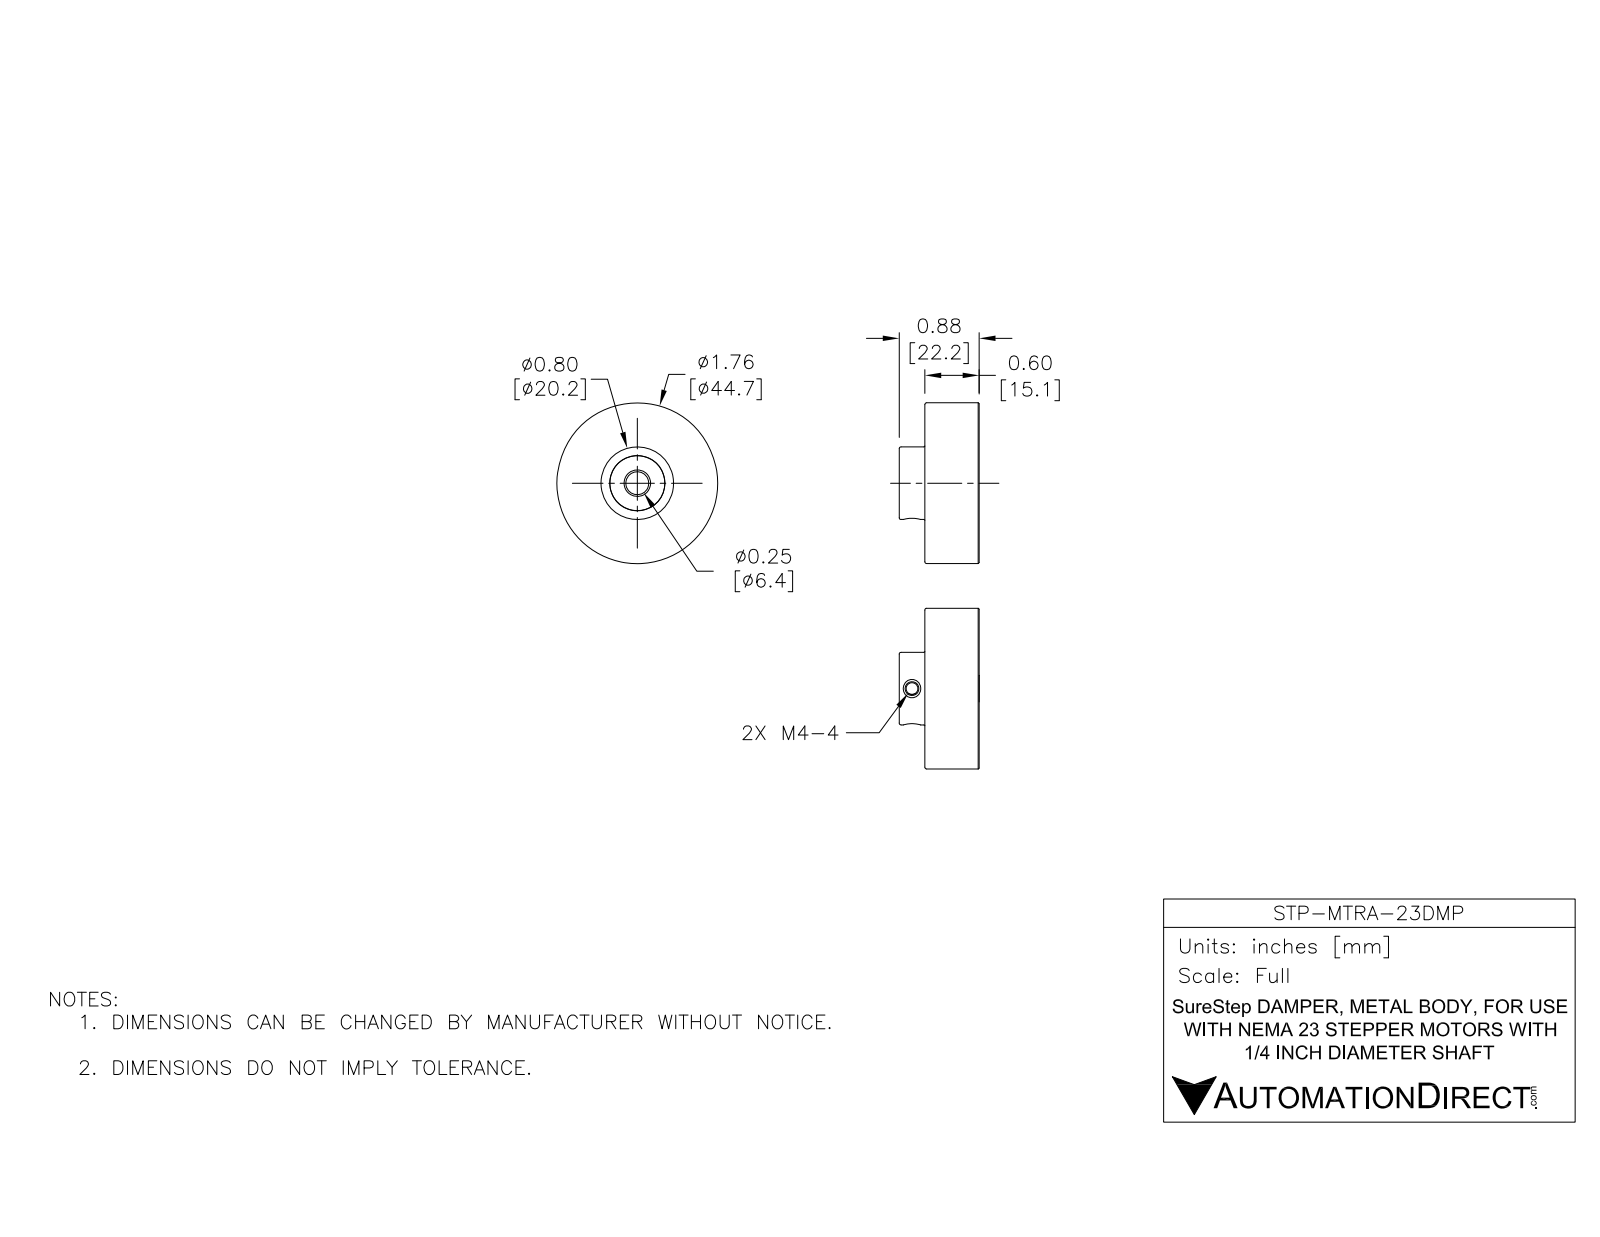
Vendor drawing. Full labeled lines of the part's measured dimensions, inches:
Part name (STEP PRODUCT): STP-MTRA-23DMP
STEP written by: SolidWorks 2017 (AUTOMOTIVE_DESIGN)
Units: inches
Bodies: 2 solids, 90 faces (13 planar, 39 cylindrical, 38 other)
Overall size (bounding box): 1.75 × 1.75 × 0.871
Volume: 0.752 in³ · Surface area: 18.38 in²
Round holes (diameter × count): ⌀0.128 ×2, ⌀0.15 ×2, ⌀0.25 ×1, ⌀0.5 ×1, ⌀0.59 ×1, ⌀0.6 ×1, ⌀1.5 ×1, ⌀1.66 ×1
Round bosses / shafts (diameter × count): ⌀1.75 ×1, ⌀1.63 ×1, ⌀1.55 ×1, ⌀0.79 ×1, ⌀0.64 ×1, ⌀0.51 ×1, ⌀0.49 ×1, ⌀0.29 ×1
Partial cylindrical surfaces — rounded edges, fillets, slot ends (radius × count): R0.335 ×1
Main face-to-face distances: 0.05, 0.541, 0.591, 0.491, 0.87, 0.82, 0.329, 0.279, 0.16, 0.11
